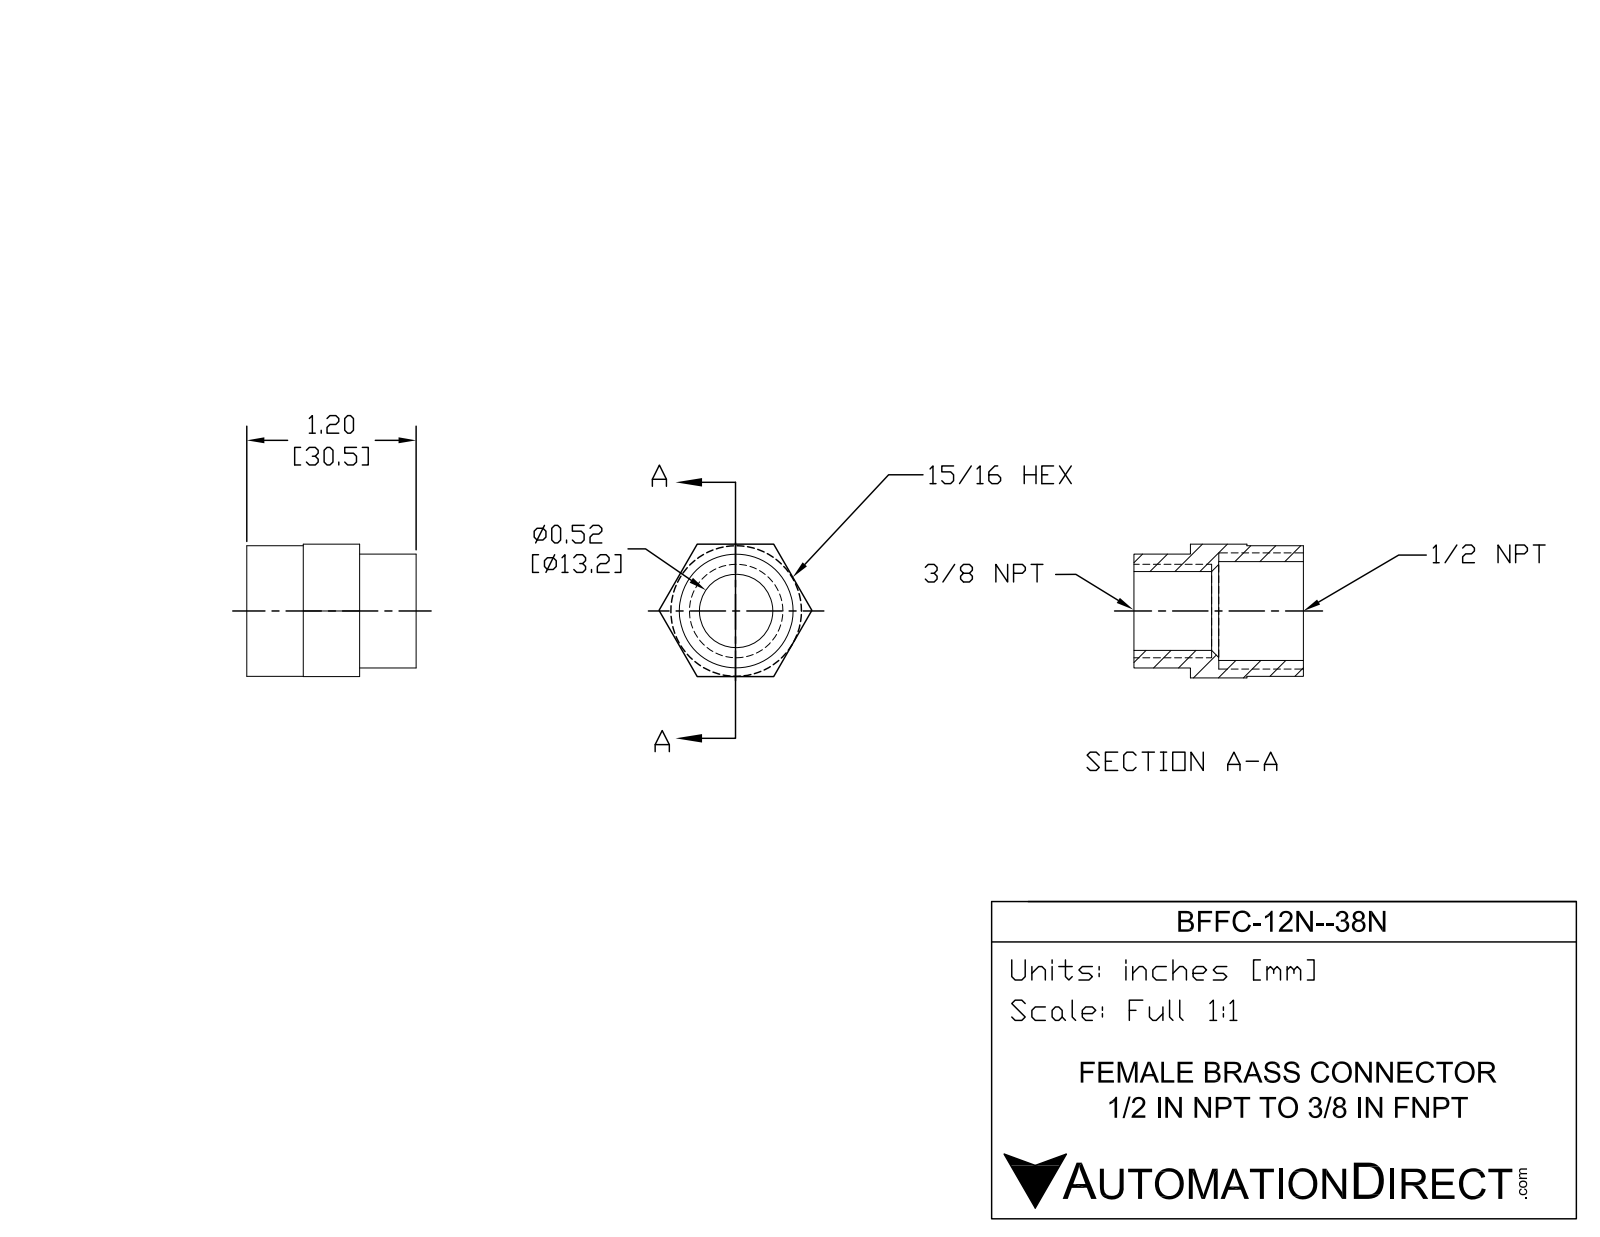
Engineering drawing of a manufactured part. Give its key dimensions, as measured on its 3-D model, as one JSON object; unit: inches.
{"part_name": "BFFC-12N-38N", "step_written_by": "SolidWorks 2015 (CONFIG_CONTROL_DESIGN)", "units": "inches", "bodies": {"solids": 1, "faces": 21, "planar": 11, "cylindrical": 8, "other": 2}, "overall_size": [1.496, 1.085, 0.94], "volume_in3": 0.481, "surface_area_in2": 8.23, "round_holes": [[0.558, 1], [0.7, 1]], "round_bosses_or_shafts": [[0.925, 1], [0.806, 1]], "face_to_face_distances": [0.94, 1.496, 0.946, 0.55, 0.546, 0.4, 0.95, 0.2, 0.746, 0.75]}
